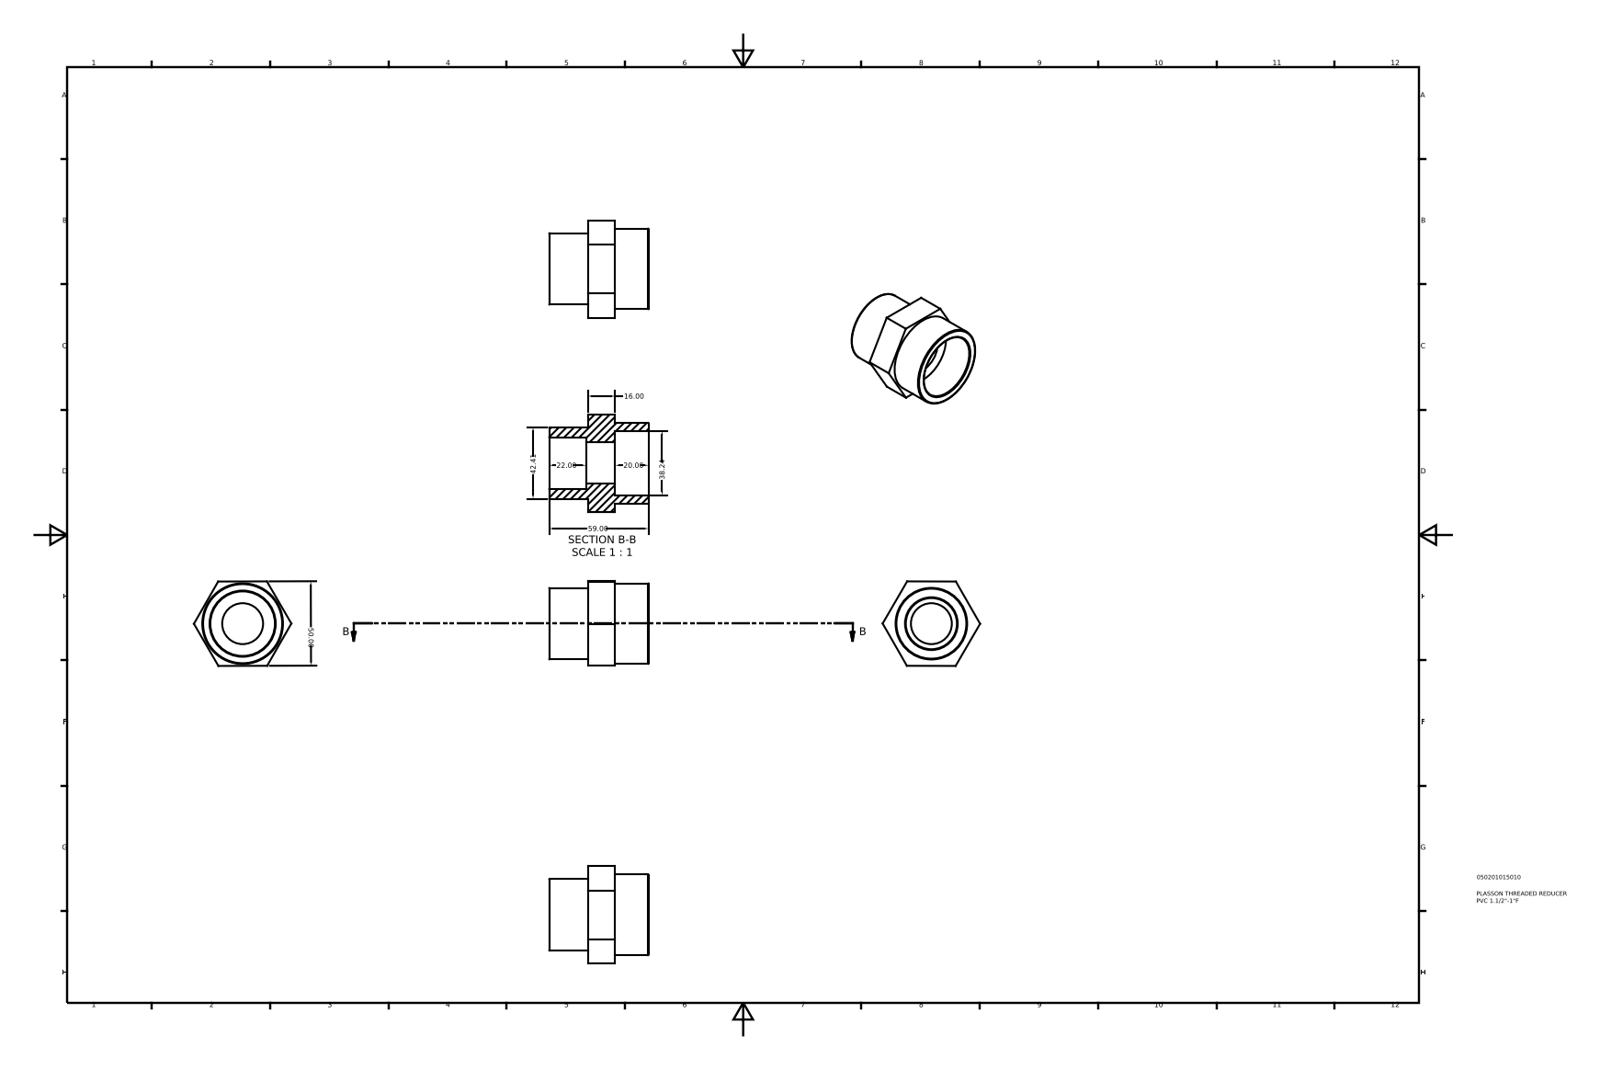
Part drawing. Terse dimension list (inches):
name: 050201015010
written by: Autodesk Inventor 2015 (AUTOMOTIVE_DESIGN)
unit: in
bodies: 1 solid, 21 faces (12 planar, 5 cylindrical, 4 other)
size: 2.323 × 2.273 × 1.972
volume: 3.437 in³; area: 27.8 in²
holes: 1× ⌀0.954, 1× ⌀1.193, 1× ⌀1.506
bosses: 1× ⌀1.882, 1× ⌀1.67
face distances: 0.63, 0.906, 1.535, 2.323, 1.417, 0.787, 1.97, 1.969, 1.969, 0.866
